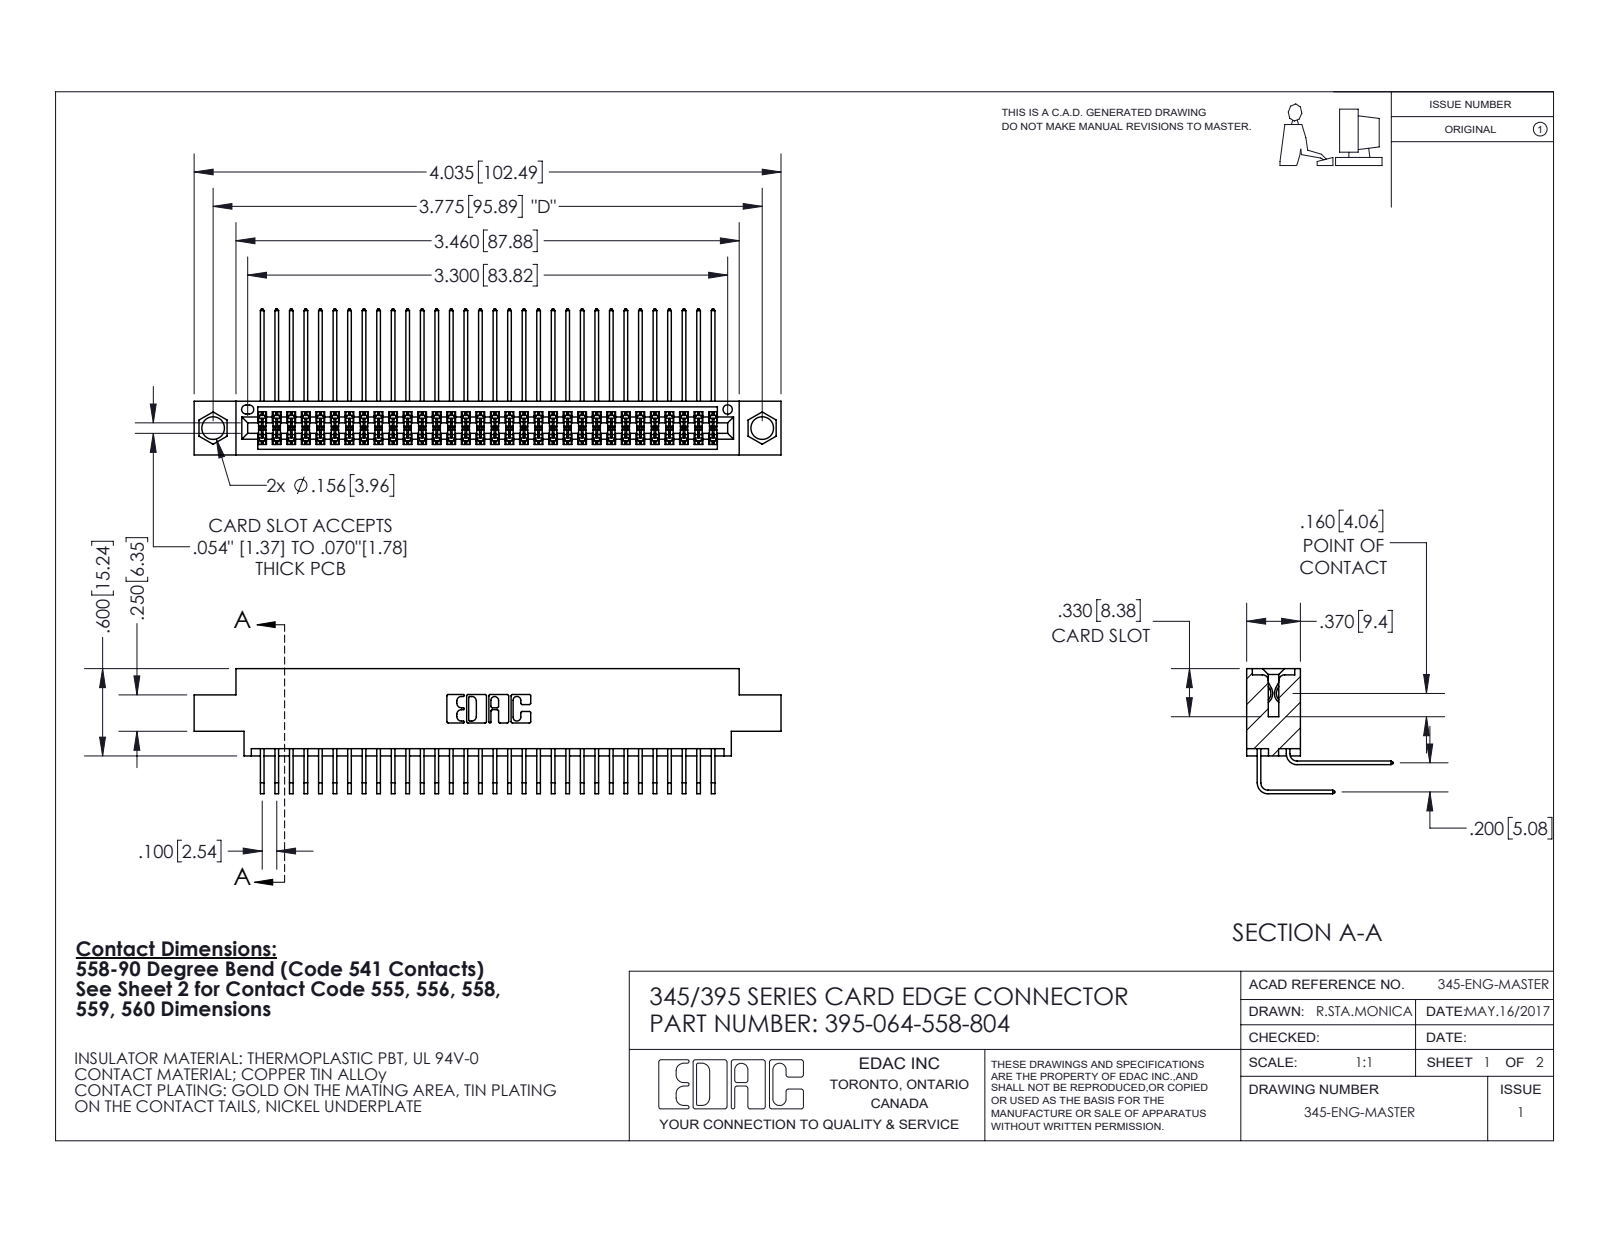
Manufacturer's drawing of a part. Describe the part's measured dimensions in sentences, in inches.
The part is named "345-292-001_558 559 Tail - 1; 395-064-558-804; 345 Part_0.170 Offset - 0.156 Dia-TI; 345-292-001_558 Tail - 2". Its 3-D file was written by "SolidWorks 2020 (CONFIG_CONTROL_DESIGN)". It is 65 solids with 3472 faces: 2338 planar, 1134 cylindrical and 0 other. Overall it measures 4.035 by 1.005 by 0.859 inches. Its volume is 0.611 cubic inches and its surface area 25.32 square inches. Round holes: 2 of diameter 0.156, 1 of diameter 0.064. Partial cylindrical surfaces (rounded edges, fillets, slot ends): 96 of radius 0.006, 22 of radius 0.01, 6 of radius 0.007, 6 of radius 0.031, 3 of radius 0.026, 2 of radius 0.014, 2 of radius 0.019, 2 of radius 0.022. The main face-to-face distances are 0.072, 0.298, 0.2, 0.37, 0.098, 0.272, 0.025, 0.225, 0.175, 0.025. The hole center spacings are 0.27, 3.54, 3.775.
